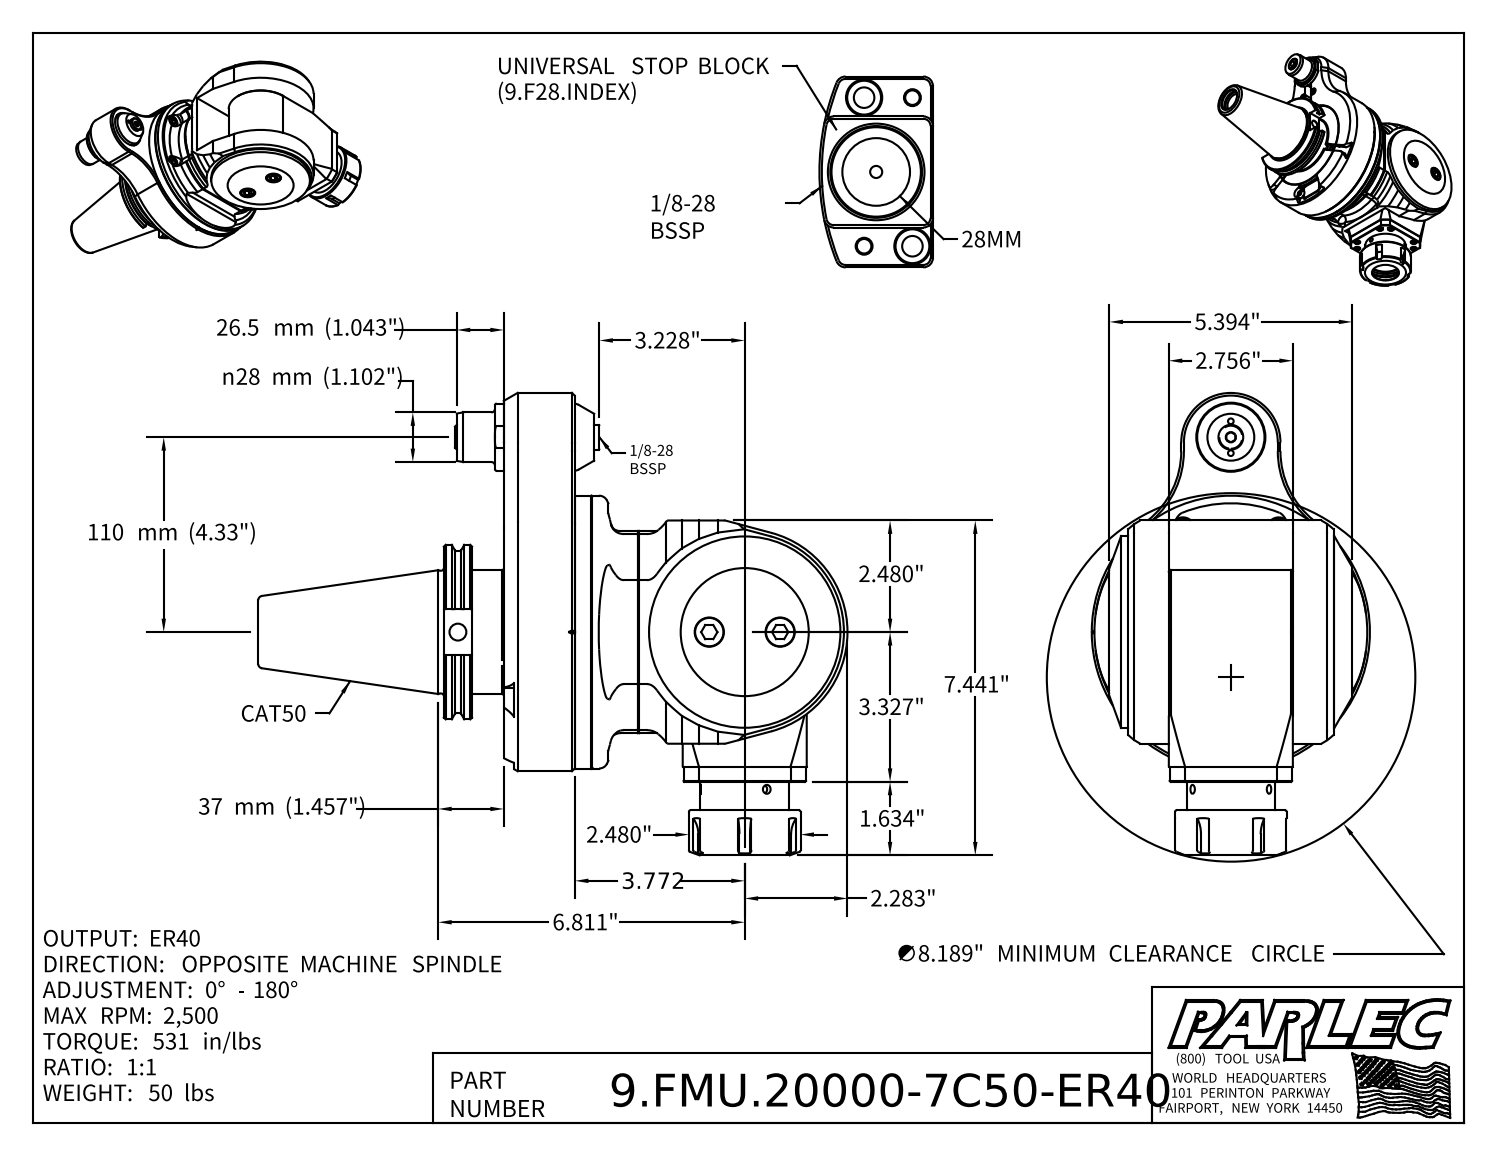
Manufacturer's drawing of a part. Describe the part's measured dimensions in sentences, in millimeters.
The part is named "9.FMU.20000-7C50-ER40; FMU-20 (ER40); 9_GA3_451_2 (Type 3, Cat50, 110. 28P)". Its 3-D file was written by "Autodesk Inventor 2022 (AUTOMOTIVE_DESIGN)". It is 4 solids with 855 faces: 400 planar, 222 cylindrical and 233 other. Overall it measures 332.6 by 261 by 157 millimeters. Its volume is 3 276 000 cubic millimeters and its surface area 335 600 square millimeters. Round holes: 8 of diameter 7.5, 4 of diameter 5, 4 of diameter 6.8, 4 of diameter 8.4, 4 of diameter 13.5, 3 of diameter 16.5, 2 of diameter 3.2, 2 of diameter 4, 2 of diameter 4.2, 2 of diameter 5.3, 2 of diameter 8, 2 of diameter 8.5. Round bosses or shafts: 8 of diameter 7, 6 of diameter 8, 4 of diameter 13, 3 of diameter 16, 2 of diameter 2.5, 1 of diameter 154, 1 of diameter 144, 1 of diameter 117.7. Partial cylindrical surfaces (rounded edges, fillets, slot ends): 8 of radius 2, 7 of radius 15, 6 of radius 3, 6 of radius 7, 4 of radius 1, 4 of radius 5, 4 of radius 10, 2 of radius 2.5. The main face-to-face distances are 35, 5, 30, 70, 6, 100.5, 95.5, 65.5, 33.5, 103.5. The hole center spacings are 50.6, 64, 13.6, 27.7, 35.7, 68.8, 70.2, 90.5.
